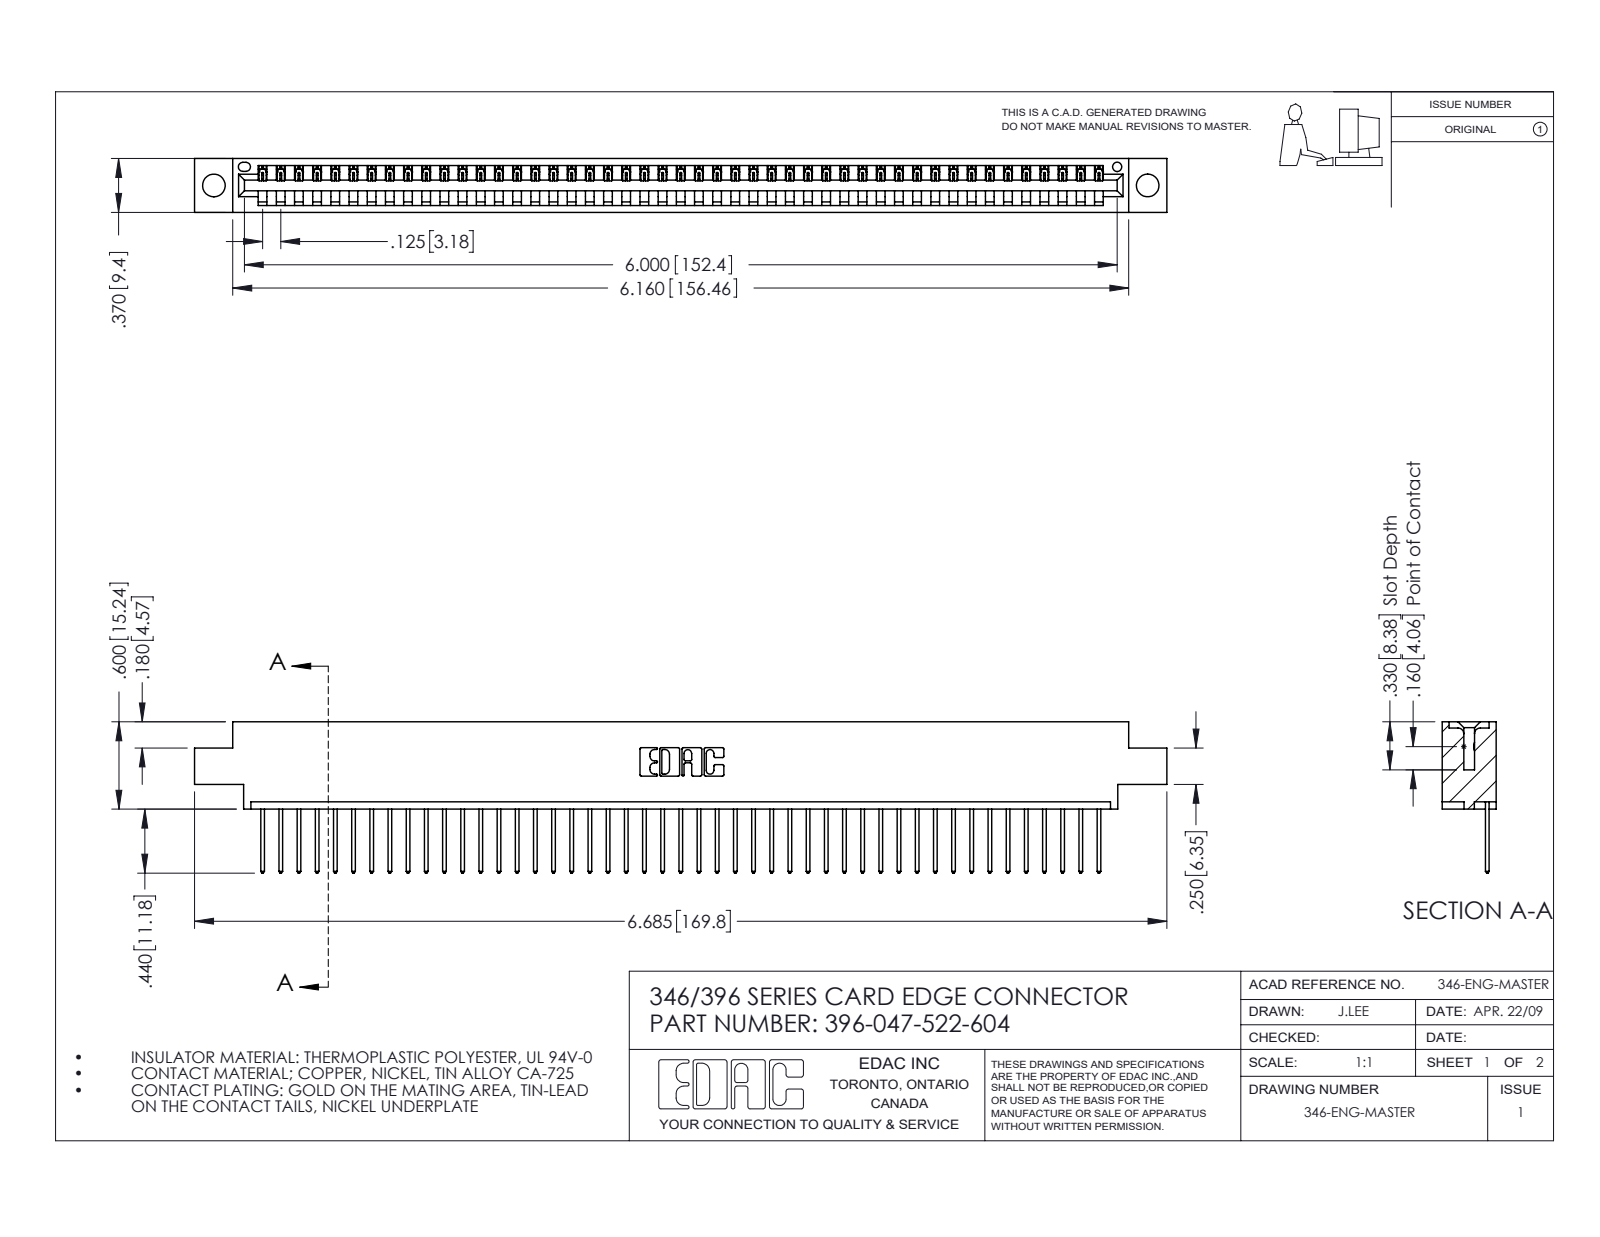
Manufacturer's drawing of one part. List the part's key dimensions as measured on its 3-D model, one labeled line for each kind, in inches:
Part name (STEP PRODUCT): 396-047-522-604; 346 Part_0.170 Offset - 0.156 Dia-TH; 345-292-001_345-293-122
STEP written by: SolidWorks 2016 (CONFIG_CONTROL_DESIGN)
Units: inches
Bodies: 48 solids, 2852 faces (1960 planar, 892 cylindrical, 0 other)
Overall size (bounding box): 6.685 × 1.04 × 0.37
Volume: 0.98 in³ · Surface area: 31.39 in²
Round holes (diameter × count): ⌀0.156 ×2, ⌀0.064 ×1
Partial cylindrical surfaces — rounded edges, fillets, slot ends (radius × count): R0.006 ×94, R0.01 ×94, R0.01 ×22, R0.007 ×6, R0.031 ×6, R0.026 ×3, R0.031 ×2, R0.04 ×2
Main face-to-face distances: 0.048, 0.322, 0.37, 0.25, 0.072, 0.298, 0.025, 0.148, 0.222, 0.1
Hole centre spacings: 0.246, 6.211, 6.42
